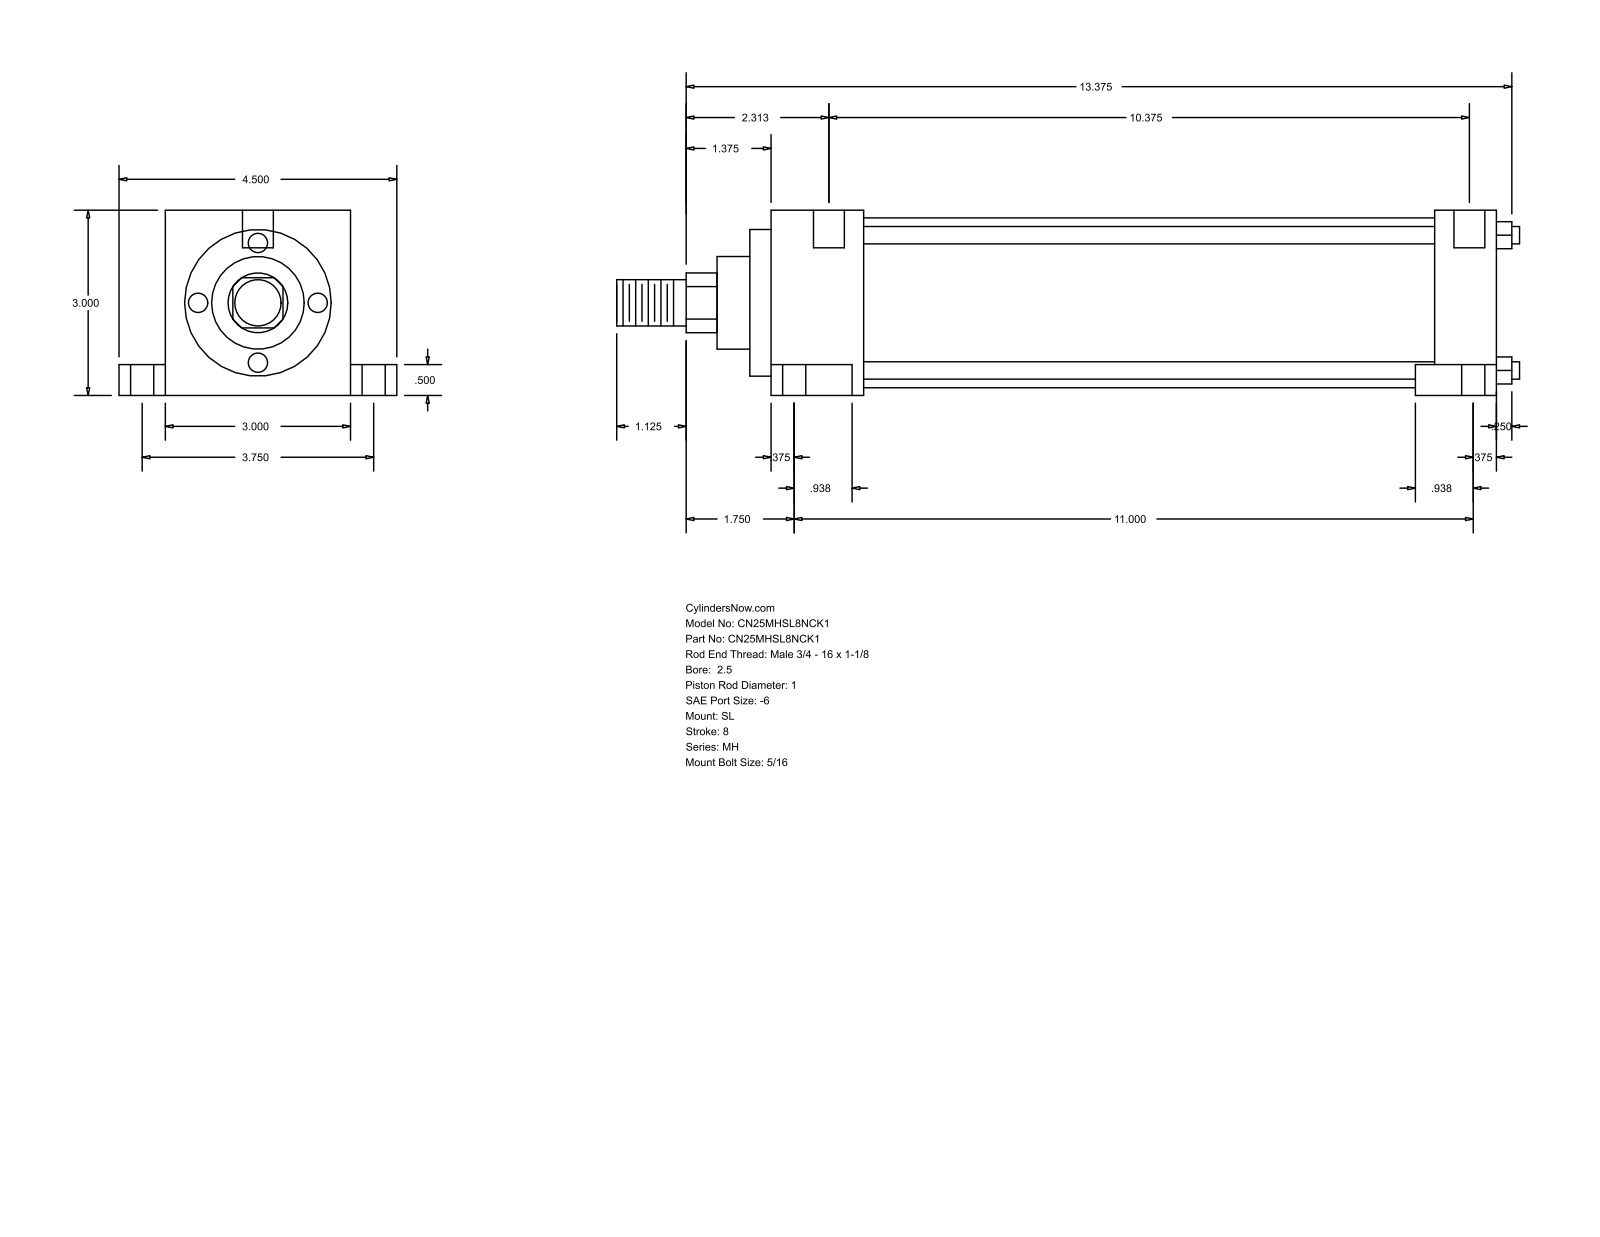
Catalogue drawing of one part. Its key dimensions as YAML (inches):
part_name: "MH_SL__0250_1"
step_written_by: "GSSL Pune (CONFIG_CONTROL_DESIGN)"
units: inches
bodies: {solids: 0, faces: 86, planar: 61, cylindrical: 25, other: 0}
overall_size: [14.625, 4.5, 3]
round_holes:
  - {diameter: 0.219, count: 2}
  - {diameter: 0.375, count: 2}
  - {diameter: 0.625, count: 2}
  - {diameter: 0.5, count: 1}
round_bosses_or_shafts:
  - {diameter: 0.281, count: 4}
  - {diameter: 2.75, count: 1}
  - {diameter: 2.375, count: 1}
  - {diameter: 1.5, count: 1}
  - {diameter: 1, count: 1}
  - {diameter: 0.75, count: 1}
partial_cylinders:
  - {radius: 0.484, count: 1}
face_to_face_distances: [3, 1, 11.094, 12.094, 0.5, 2.5, 0.75, 3.75, 0.531, 11.625]
hole_center_spacings: [1.876, 0.125, 3.75]
